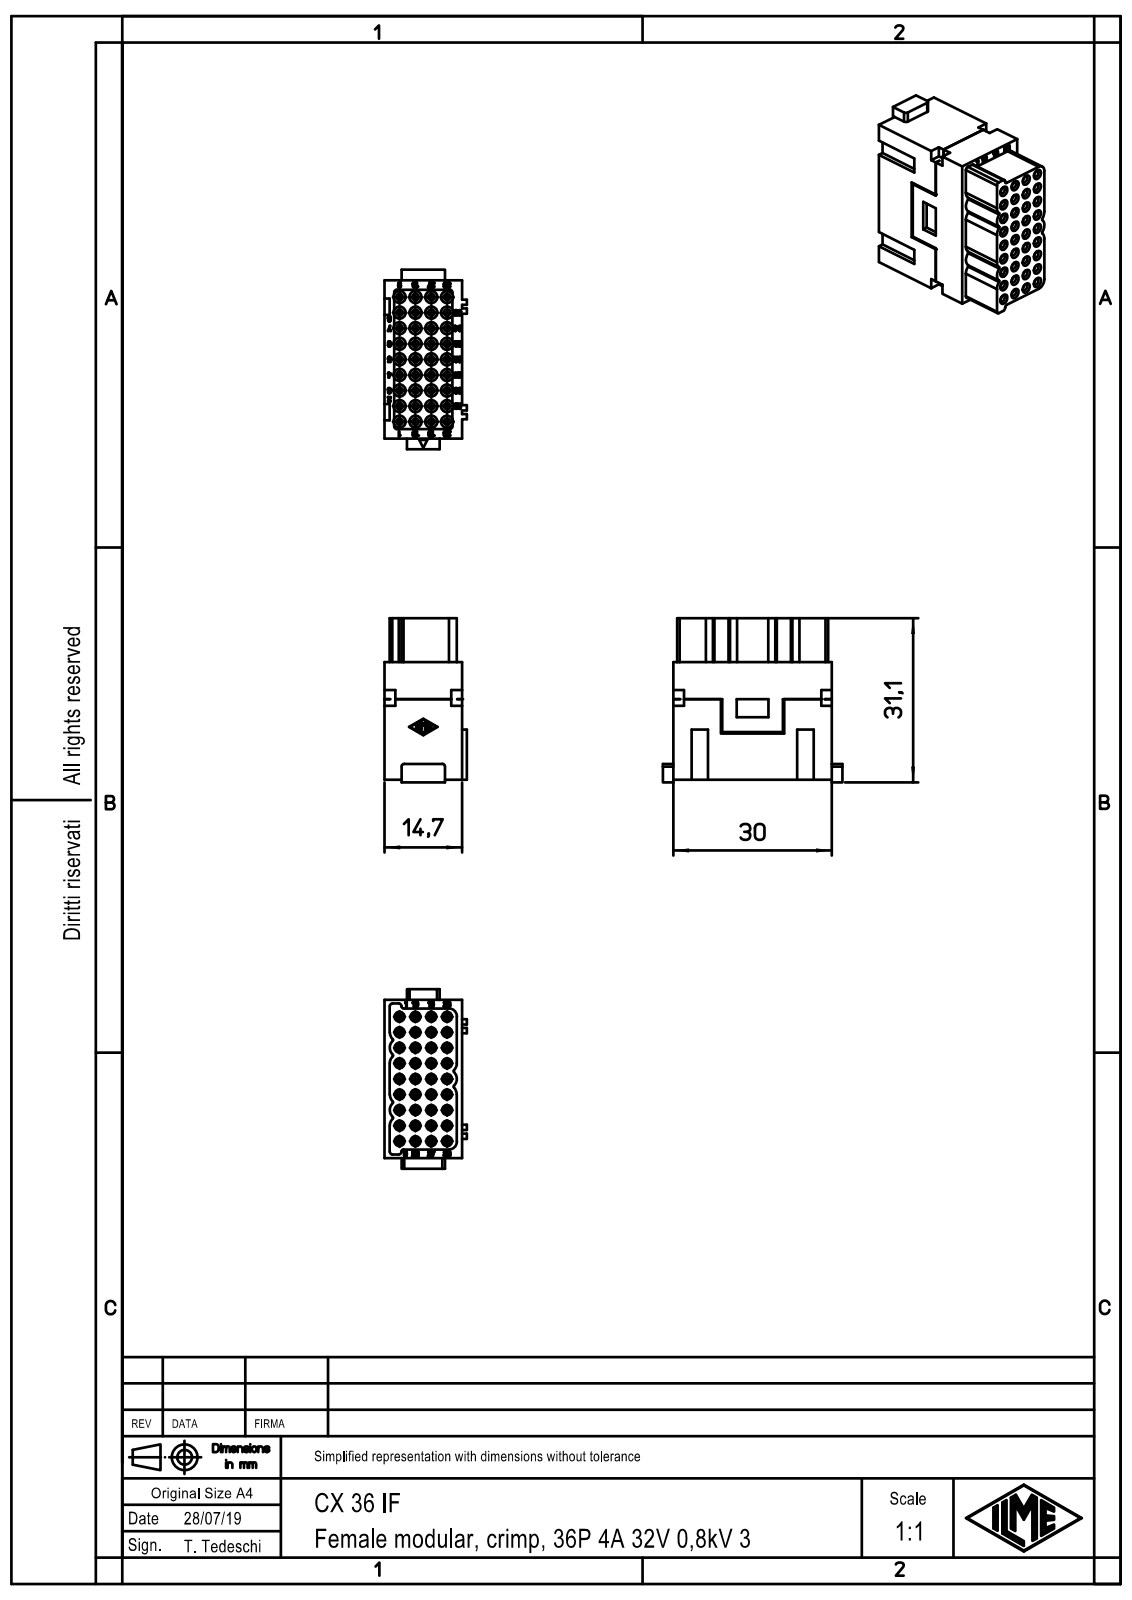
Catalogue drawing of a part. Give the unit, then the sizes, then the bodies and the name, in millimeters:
Units: millimetres
Overall size (bounding box): 34 × 31.1 × 15.6
Round holes (diameter × count): ⌀1.2 ×36, ⌀2.3 ×36
Partial cylindrical surfaces — rounded edges, fillets, slot ends (radius × count): R0.5 ×12, R1.85 ×9, R0.2 ×6, R0.1 ×5, R0.4 ×2, R1.5 ×2
Main face-to-face distances: 14.7, 1.85, 12.85, 1, 11.85, 0.85, 13.7, 30, 1.8, 28.2
Hole centre spacings: 4.21, 6.62, 9.34, 6.69, 2.95, 5.9, 8.41, 12.18
Volume: 6 297 mm³ · Surface area: 9 350 mm²
Bodies: 1 solid, 3066 faces (2805 planar, 180 cylindrical, 81 other)
Part name (STEP PRODUCT): CX_36_IF
STEP written by: Creo Elements/Direct Modeling 20.1B 02-Apr-2019 (C) Parametric Technology GmbH (AUTOMOTIVE_DESIGN)
